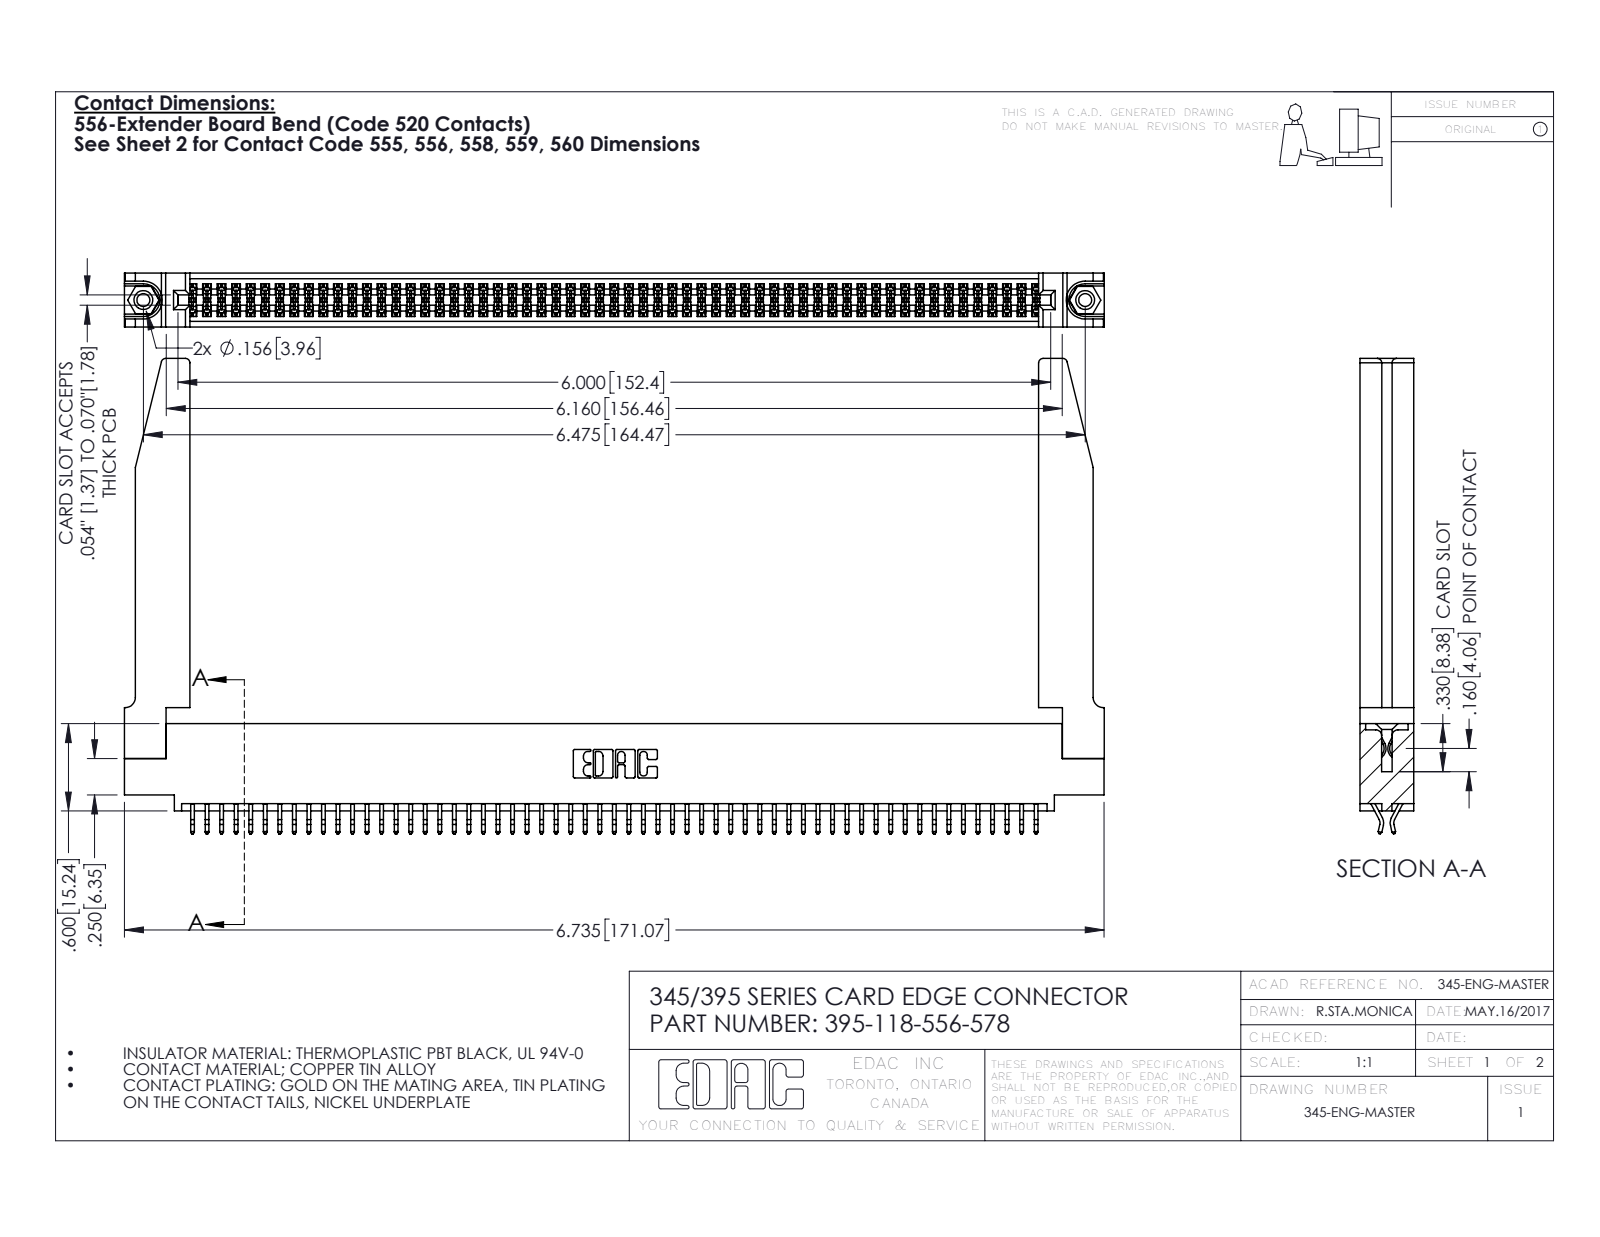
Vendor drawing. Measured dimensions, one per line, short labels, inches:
name: 345 Part_0.110 Offset - 0.156 Dia-TH; 345-250-001_345-250-001-102; 395-118-556-578; 345-220-078_345-220-078 (+1 more)
written by: SolidWorks 2016 (CONFIG_CONTROL_DESIGN)
unit: in
bodies: 123 solids, 6972 faces (4592 planar, 2328 cylindrical, 52 other)
size: 6.736 × 3.267 × 0.37
volume: 1.493 in³; area: 49.36 in²
holes: 2× ⌀0.089, 2× ⌀0.125, 2× ⌀0.156, 1× ⌀0.064
bosses: 2× ⌀0.155
rounds: 177× R0.006, 22× R0.01, 8× R0.03, 6× R0.007, 6× R0.031, 3× R0.026, 2× R0.01, 2× R0.014
face distances: 0.072, 0.37, 0.298, 0.025, 0.098, 0.272, 0.2, 0.225, 0.175, 0.148
hole spacings: 0.27, 6.239, 6.475
